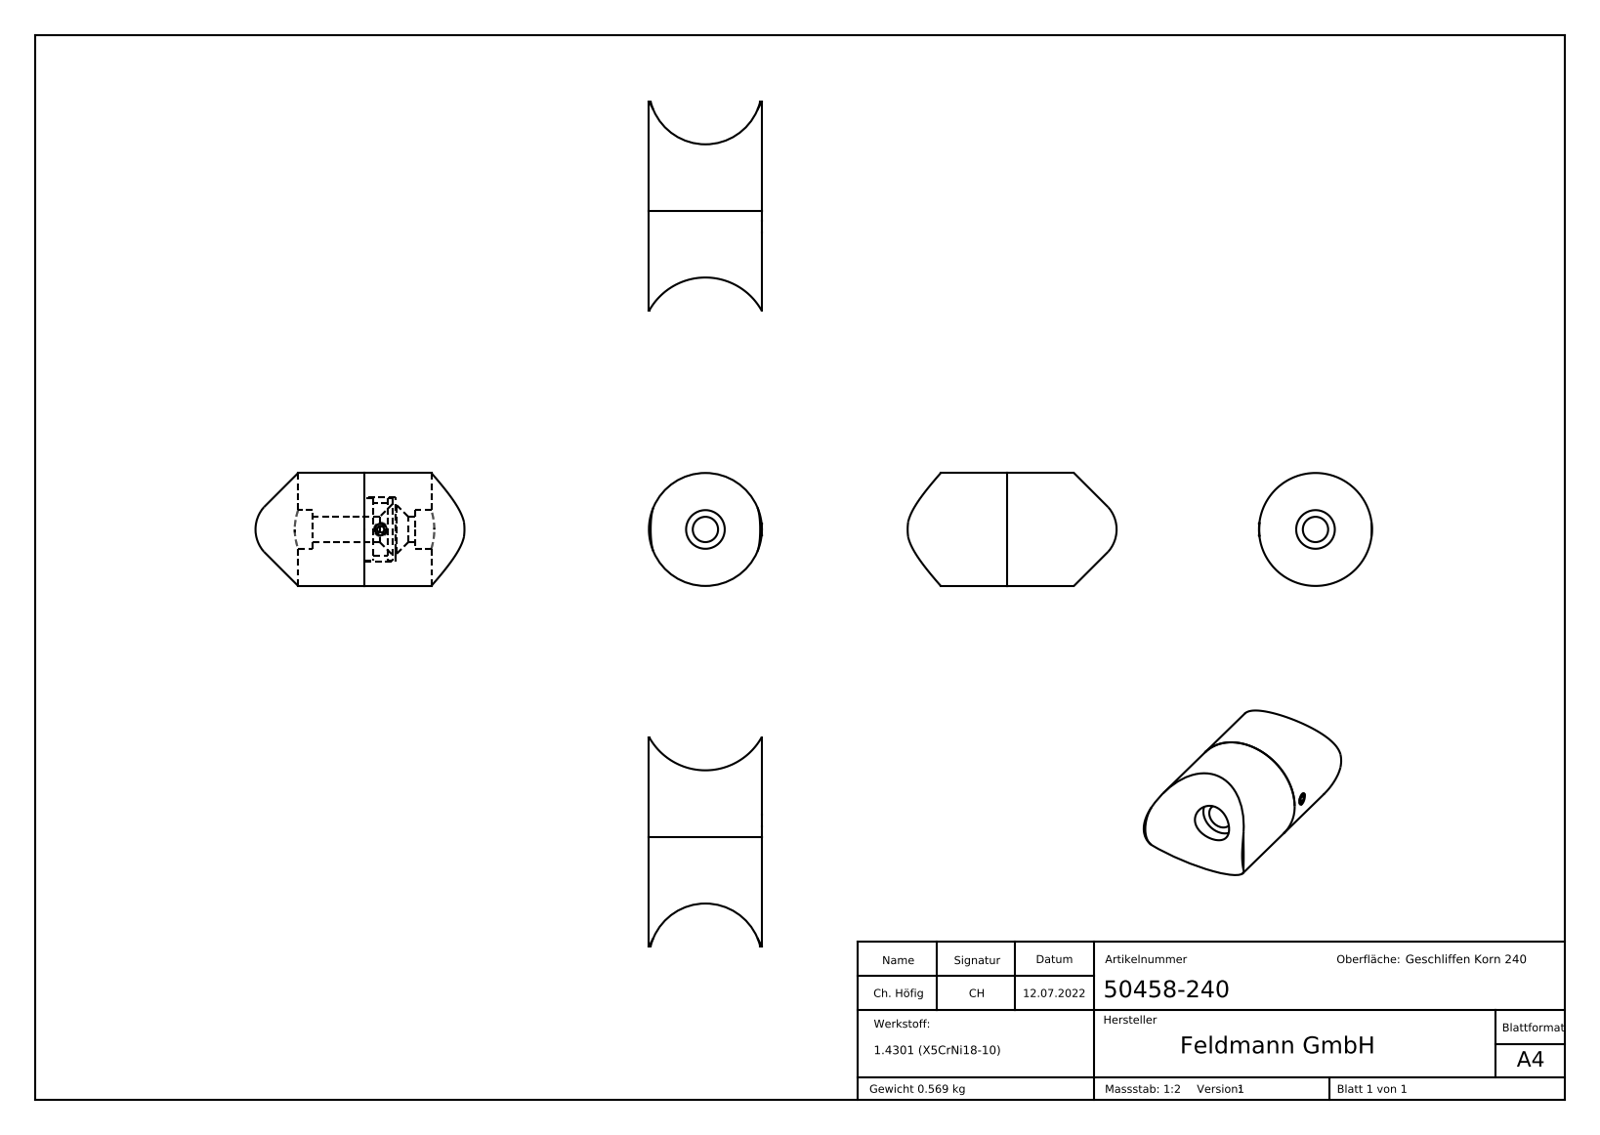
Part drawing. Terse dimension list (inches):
name: 50458-240 Teil1_50458-240 Teil1; 50458-240 DIN913 M5x10_DIN913 M5x10; 50458-240 Teil2_50458-240 Teil2; 50458-240
written by: SolidWorks 2018 (CONFIG_CONTROL_DESIGN)
unit: in
bodies: 3 solids, 273 faces (145 planar, 19 cylindrical, 109 other)
size: 3.088 × 1.669 × 1.669
volume: 4.392 in³; area: 27.97 in²
holes: 1× ⌀0.165, 1× ⌀0.374, 1× ⌀0.571, 1× ⌀0.719, 1× ⌀0.945
bosses: 1× ⌀1.669, 1× ⌀0.935, 1× ⌀0.778, 1× ⌀0.197
rounds: 1× R0.497, 1× R0.833, 1× R0.835, 1× R0.951
face distances: 0.453, 0.039, 0.413, 0.106, 0.067, 0.346, 0.323, 0.283, 0.217, 0.13
